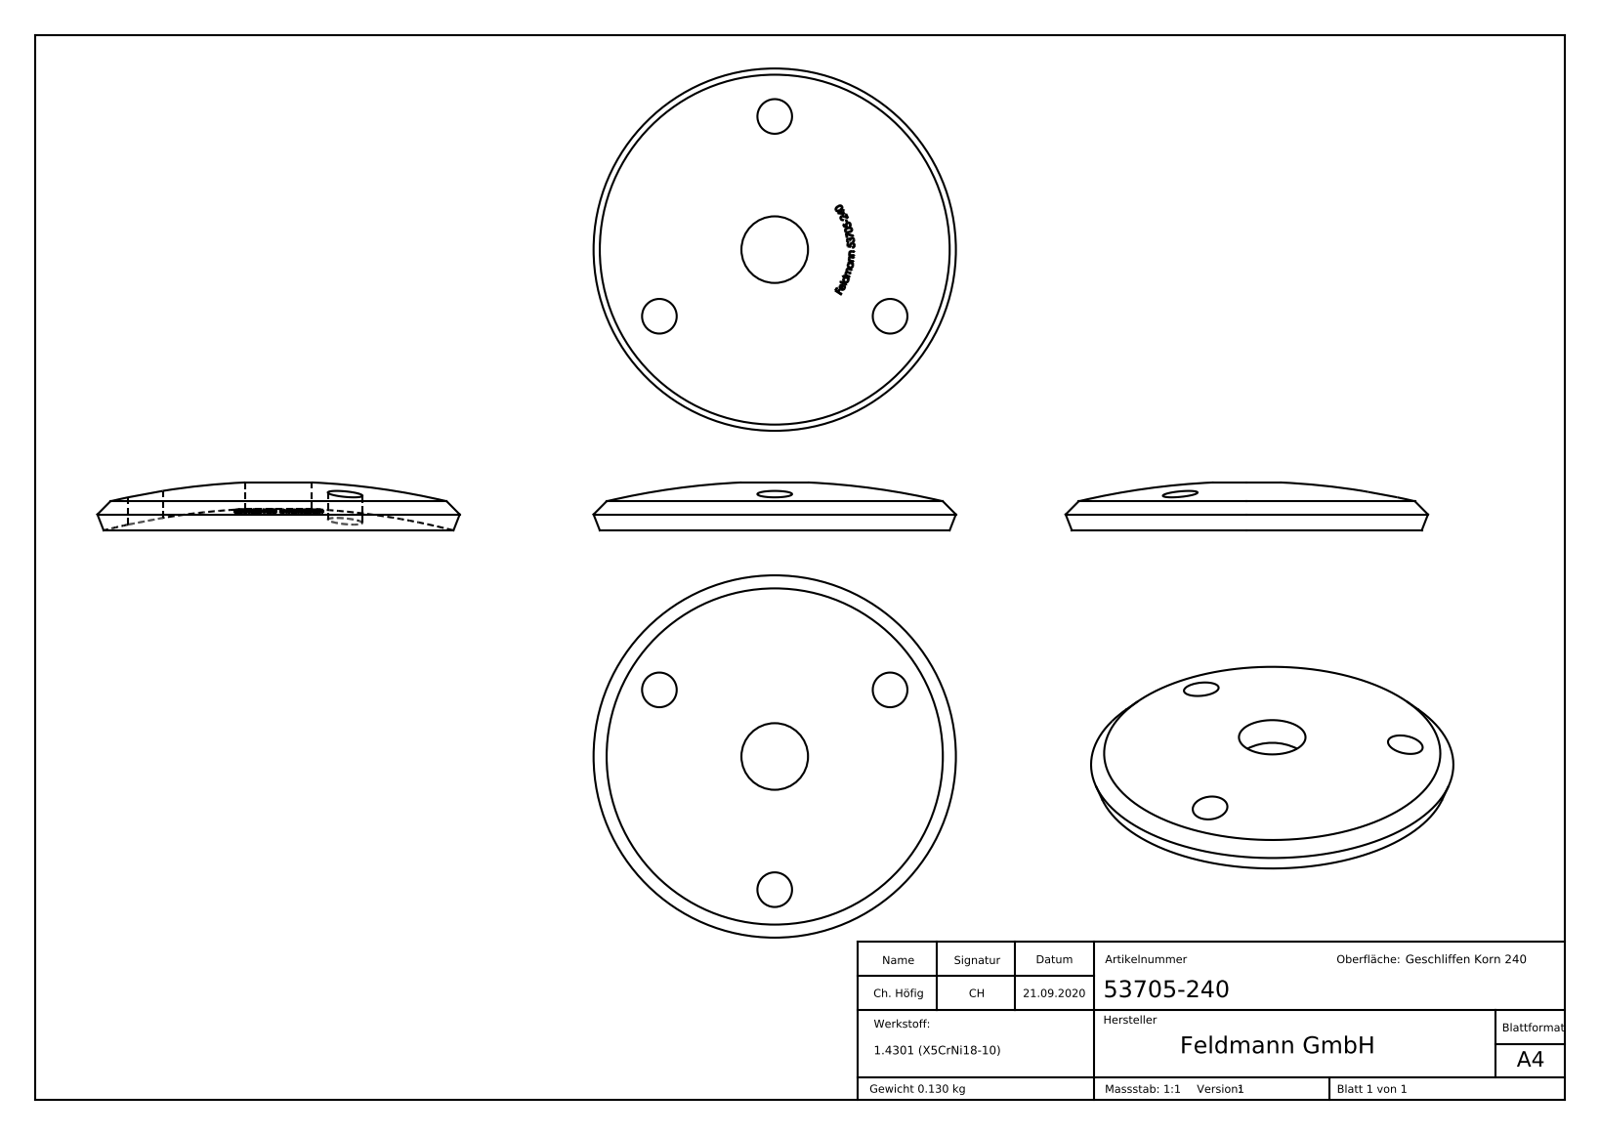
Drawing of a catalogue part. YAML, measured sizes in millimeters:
part_name: "53705-240"
step_written_by: "SolidWorks 2018 (CONFIG_CONTROL_DESIGN)"
units: millimeters
bodies: {solids: 1, faces: 239, planar: 98, cylindrical: 8, other: 133}
overall_size: [68, 68, 9]
volume: 16448
surface_area: 8110
round_holes:
  - {diameter: 6.5, count: 3}
  - {diameter: 12.5, count: 1}
face_to_face_distances: [0.72, 0.54, 0.67, 0.79, 0.41, 0.85, 0.73, 0.97, 0.66, 0.6]
hole_center_spacings: [25, 43.3]
